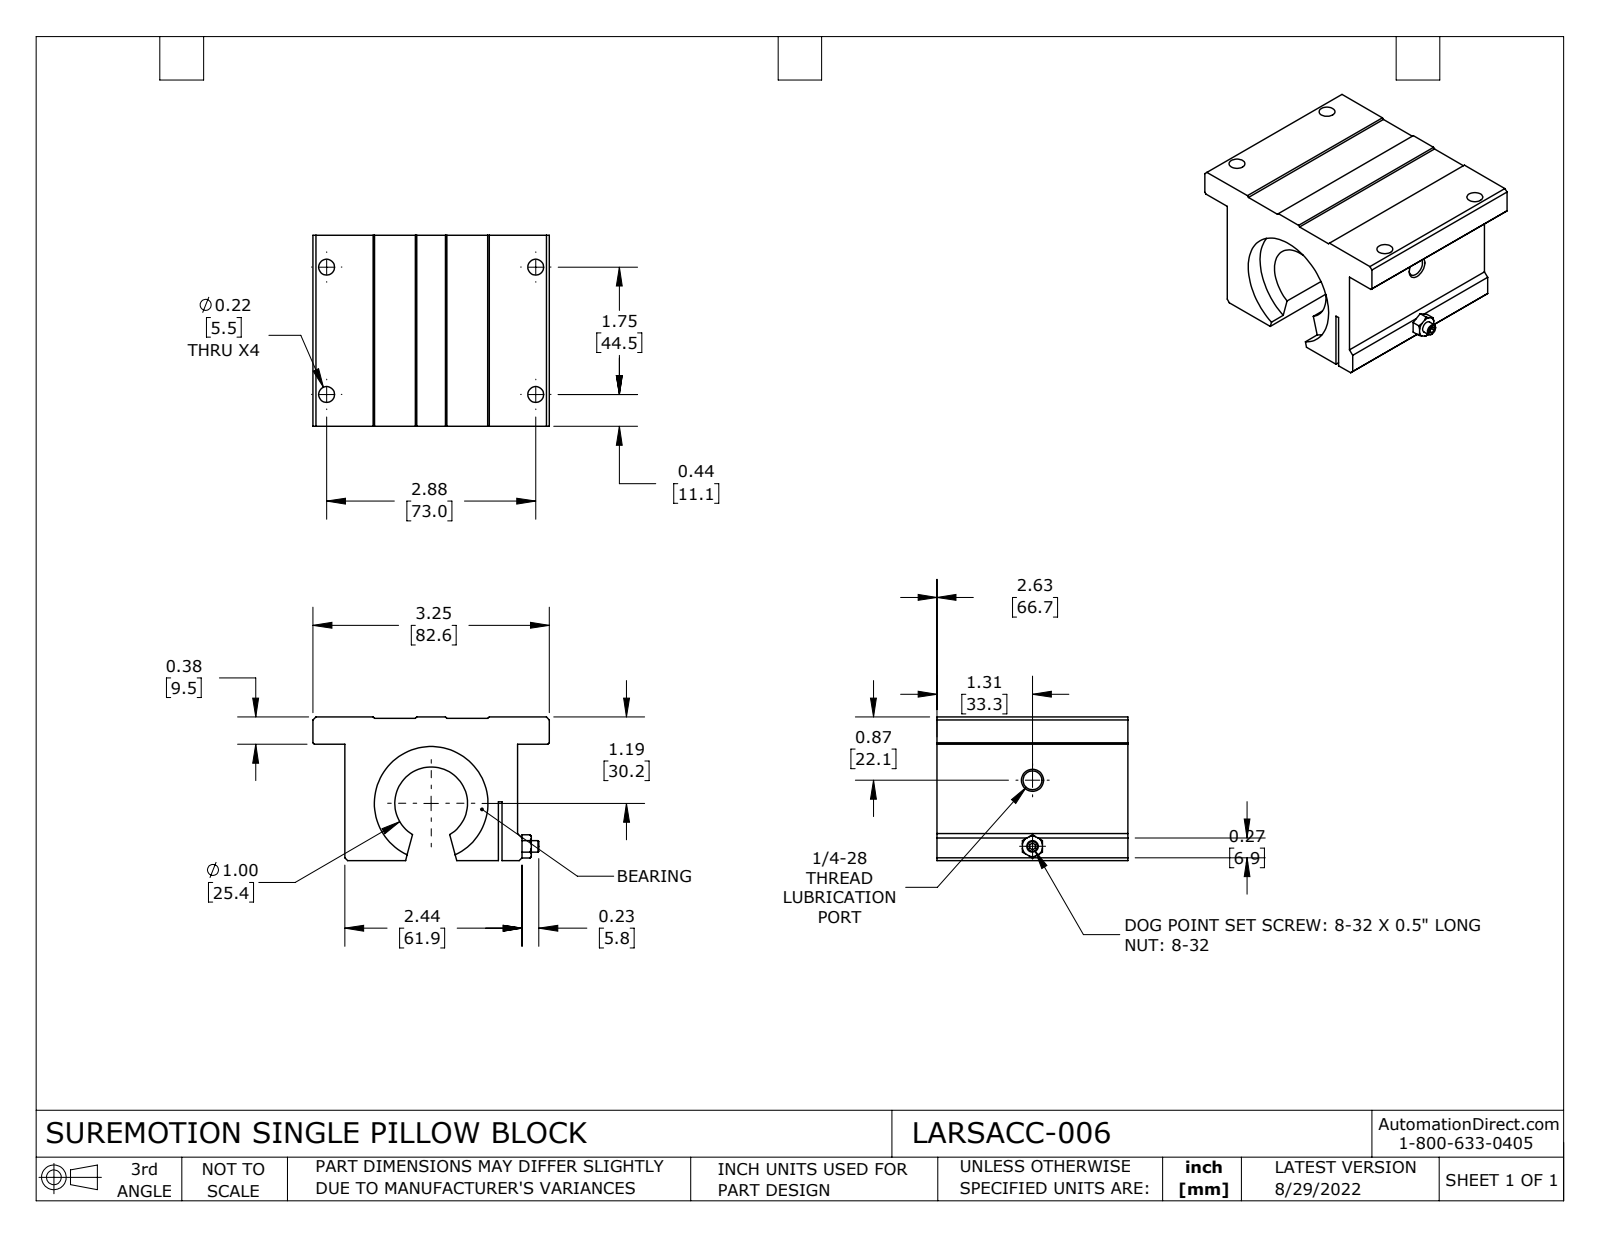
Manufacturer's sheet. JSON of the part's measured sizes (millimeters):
{"part_name": "LARSACC-006", "step_written_by": "SolidWorks 2021 (CONFIG_CONTROL_DESIGN)", "units": "millimeters", "bodies": {"solids": 2, "faces": 83, "planar": 52, "cylindrical": 21, "other": 10}, "overall_size": [82.6, 66.7, 50.2], "volume_mm3": 163700, "surface_area_mm2": 31230, "round_holes": [[5.5, 4], [6.6, 1], [25.4, 1], [39.7, 1]], "round_bosses_or_shafts": [[4, 1]], "face_to_face_distances": [50.2, 60.4, 66.7, 49.7, 0.5, 9.5, 54.9, 5.4, 53.7, 1.3], "hole_center_spacings": [44.5, 73, 85.5]}
